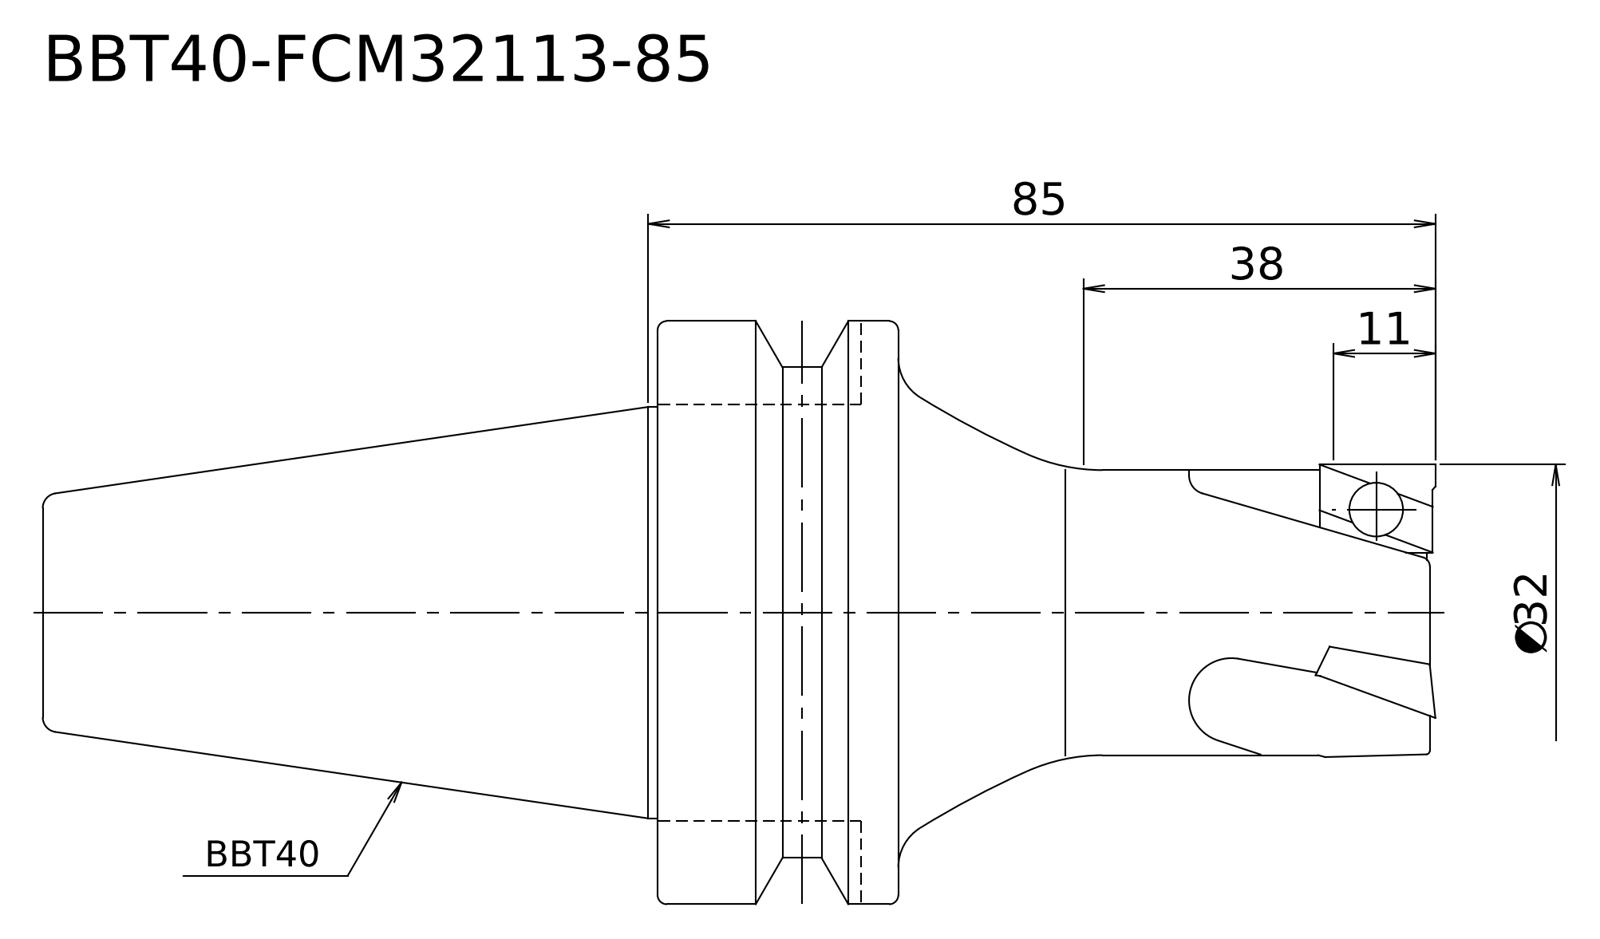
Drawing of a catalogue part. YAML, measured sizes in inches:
step_written_by: "Kubotek KeyCreator V8.5.1 (14335) (CONFIG_CONTROL_DESIGN)"
units: inches
bodies: {solids: 1, faces: 17, planar: 4, cylindrical: 6, other: 7}
overall_size: [5.921, 2.48, 2.48]
volume: 11.85
surface_area: 36.89
round_bosses_or_shafts:
  - {diameter: 2.48, count: 1}
  - {diameter: 2.087, count: 1}
  - {diameter: 1.75, count: 1}
  - {diameter: 1.26, count: 1}
  - {diameter: 1.213, count: 1}
face_to_face_distances: [3.307, 2.283, 1.024, 5.921, 3.638, 2.614]
